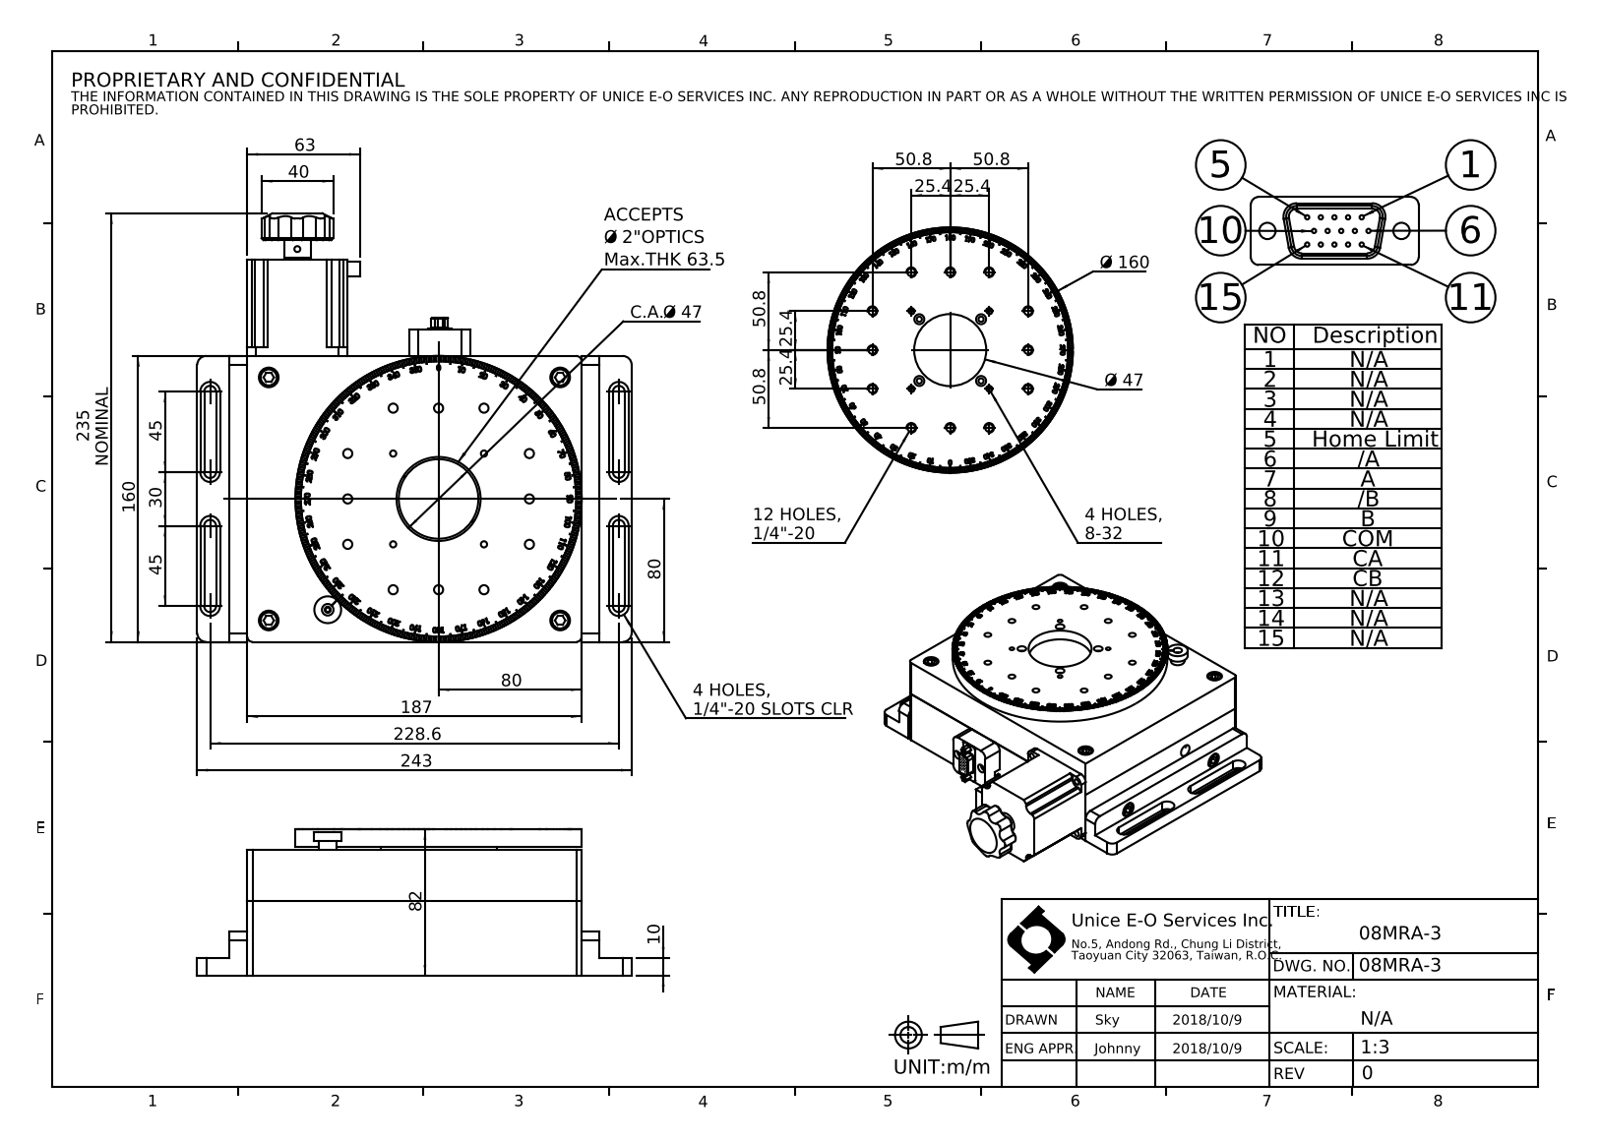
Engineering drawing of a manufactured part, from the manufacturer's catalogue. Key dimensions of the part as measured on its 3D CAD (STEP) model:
Part name (STEP PRODUCT): 08MRA-3
STEP written by: SolidWorks 2016 (AUTOMOTIVE_DESIGN)
Units: millimetres
Bodies: 0 solids, 1054 faces (726 planar, 239 cylindrical, 89 other)
Overall size (bounding box): 243 × 239.8 × 82
Round holes (diameter × count): ⌀0.8 ×14, ⌀5.11 ×12, ⌀6.5 ×7, ⌀3.4 ×6, ⌀11 ×6, ⌀3.45 ×4, ⌀4.5 ×4, ⌀1.5 ×2, ⌀2.5 ×2, ⌀5 ×2, ⌀9 ×1, ⌀44.5 ×1
Round bosses / shafts (diameter × count): ⌀10 ×4, ⌀15 ×2, ⌀160 ×1, ⌀85 ×1
Partial cylindrical surfaces — rounded edges, fillets, slot ends (radius × count): R5 ×14, R3.3 ×8, R4 ×8, R5.5 ×8, R7.41 ×8, R0.5 ×7, R1.5 ×4, R2 ×4
Main face-to-face distances: 10, 70.5, 42, 28.5, 72, 1.5, 82, 40, 11.5, 30
Hole centre spacings: 56.8, 2.84, 25.4, 35.92, 80.32, 91.58, 4.58, 5.08
